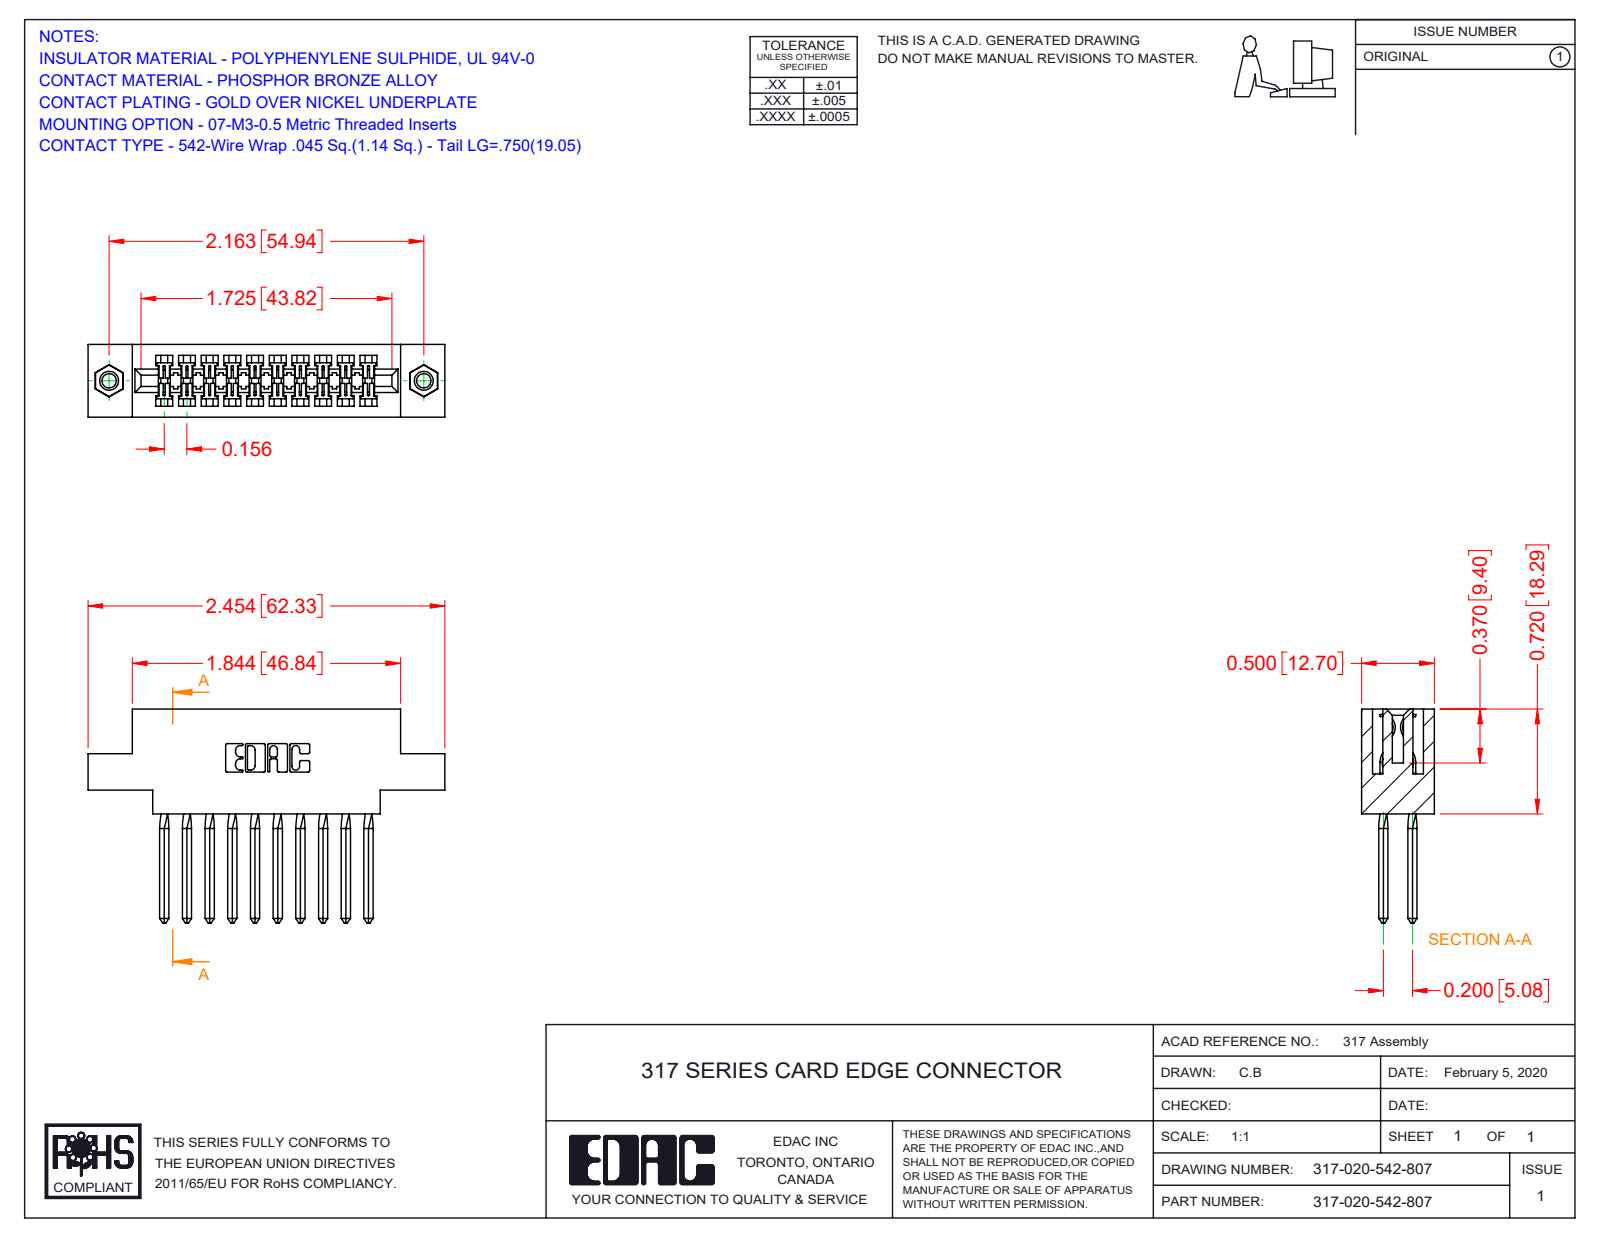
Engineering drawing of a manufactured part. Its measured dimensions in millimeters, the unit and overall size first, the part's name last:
Units: millimetres
Overall size (bounding box): 62.3 × 37.3 × 12.7
Round holes (diameter × count): ⌀2.5 ×2, ⌀3.2 ×2, ⌀4 ×2
Round bosses / shafts (diameter × count): ⌀3.9 ×2
Partial cylindrical surfaces — rounded edges, fillets, slot ends (radius × count): R0.2 ×40, R0.3 ×22, R0.2 ×6, R0.8 ×6, R0.7 ×3, R1.9 ×2, R2.3 ×2, R2.5 ×2
Main face-to-face distances: 12.7, 1.9, 10.8, 2.8, 5.6, 2.9, 8.9, 3.5, 4, 5.1
Hole centre spacings: 54.9
Volume: 9 180 mm³ · Surface area: 11 780 mm²
Bodies: 23 solids, 1302 faces (1010 planar, 196 cylindrical, 96 other)
Part name (STEP PRODUCT): 317-290-003_542; 317-020-542-807; 345-250-001_345-250-005-103; 317 Part_.156 Dia - TI
STEP written by: SolidWorks 2016 (CONFIG_CONTROL_DESIGN)
